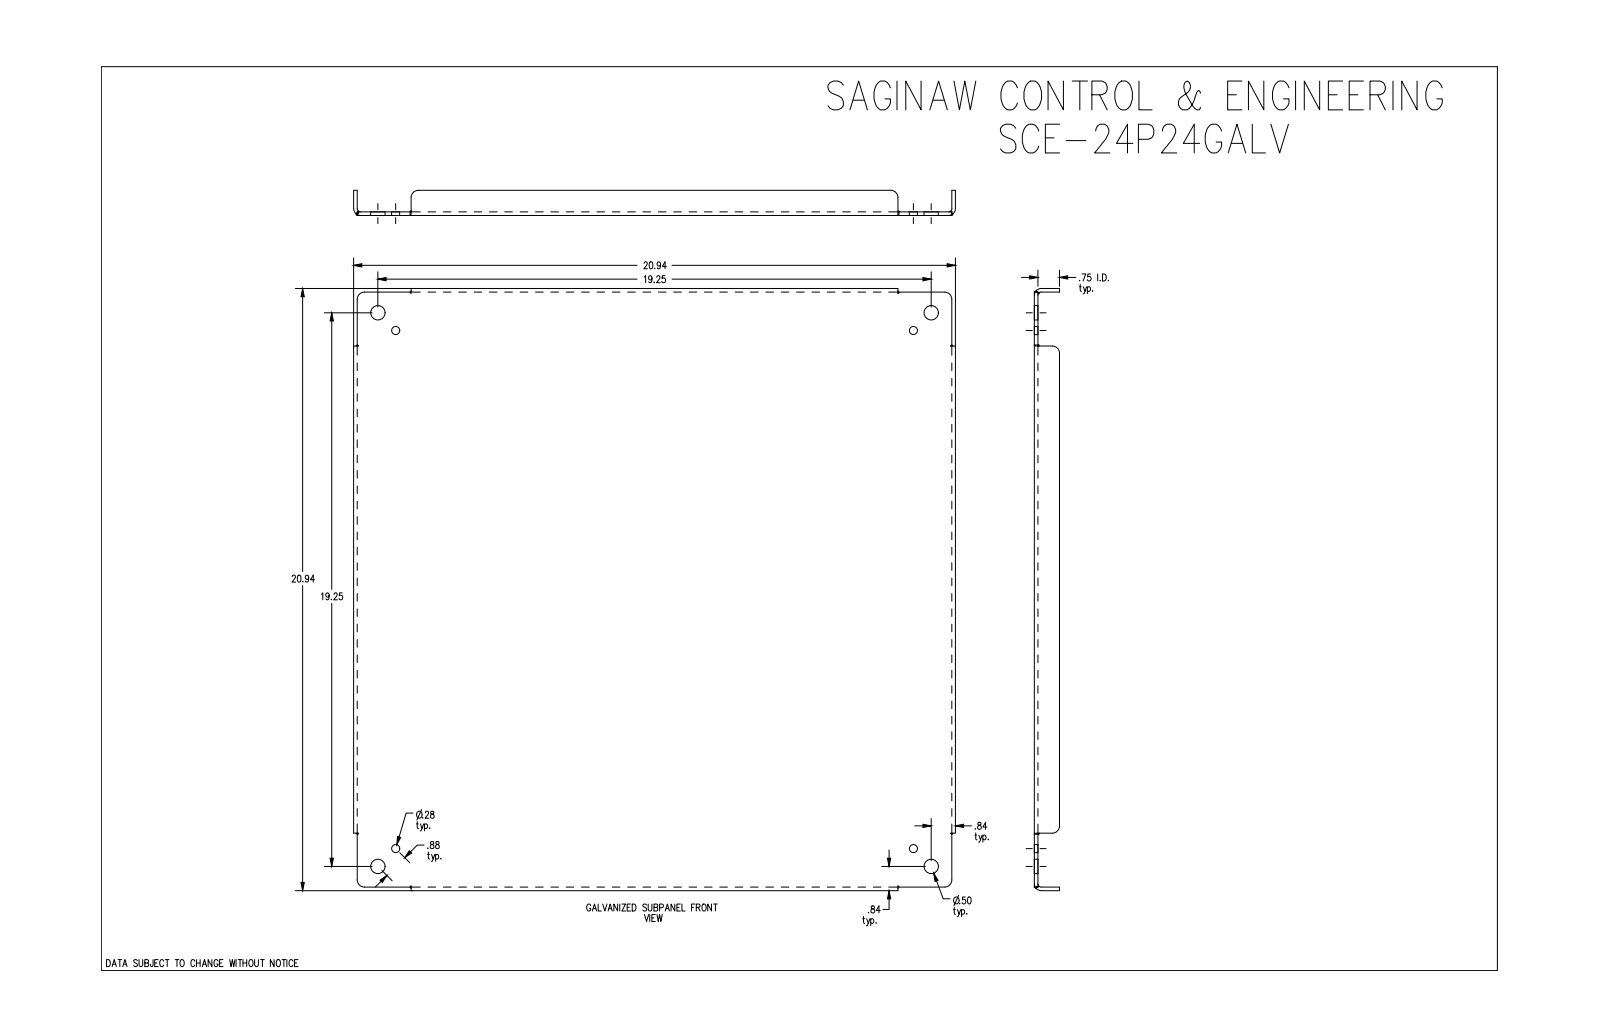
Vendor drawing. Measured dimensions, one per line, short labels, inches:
name: SCE-24P24GALV
written by: SolidWorks 2019 (CONFIG_CONTROL_DESIGN)
unit: in
bodies: 1 solid, 82 faces (30 planar, 28 cylindrical, 24 other)
size: 20.938 × 20.938 × 0.875
volume: 60.12 in³; area: 974.2 in²
holes: 4× ⌀0.281, 4× ⌀0.5
rounds: 8× R0.25, 4× R0.112, 4× R0.237
face distances: 0.125, 0.125, 20.813, 20.687, 20.938, 0.75, 0.875, 2, 18.938, 1.875
hole spacings: 18.641, 0.875, 18.013, 19.25, 26.348, 25.474, 27.223
